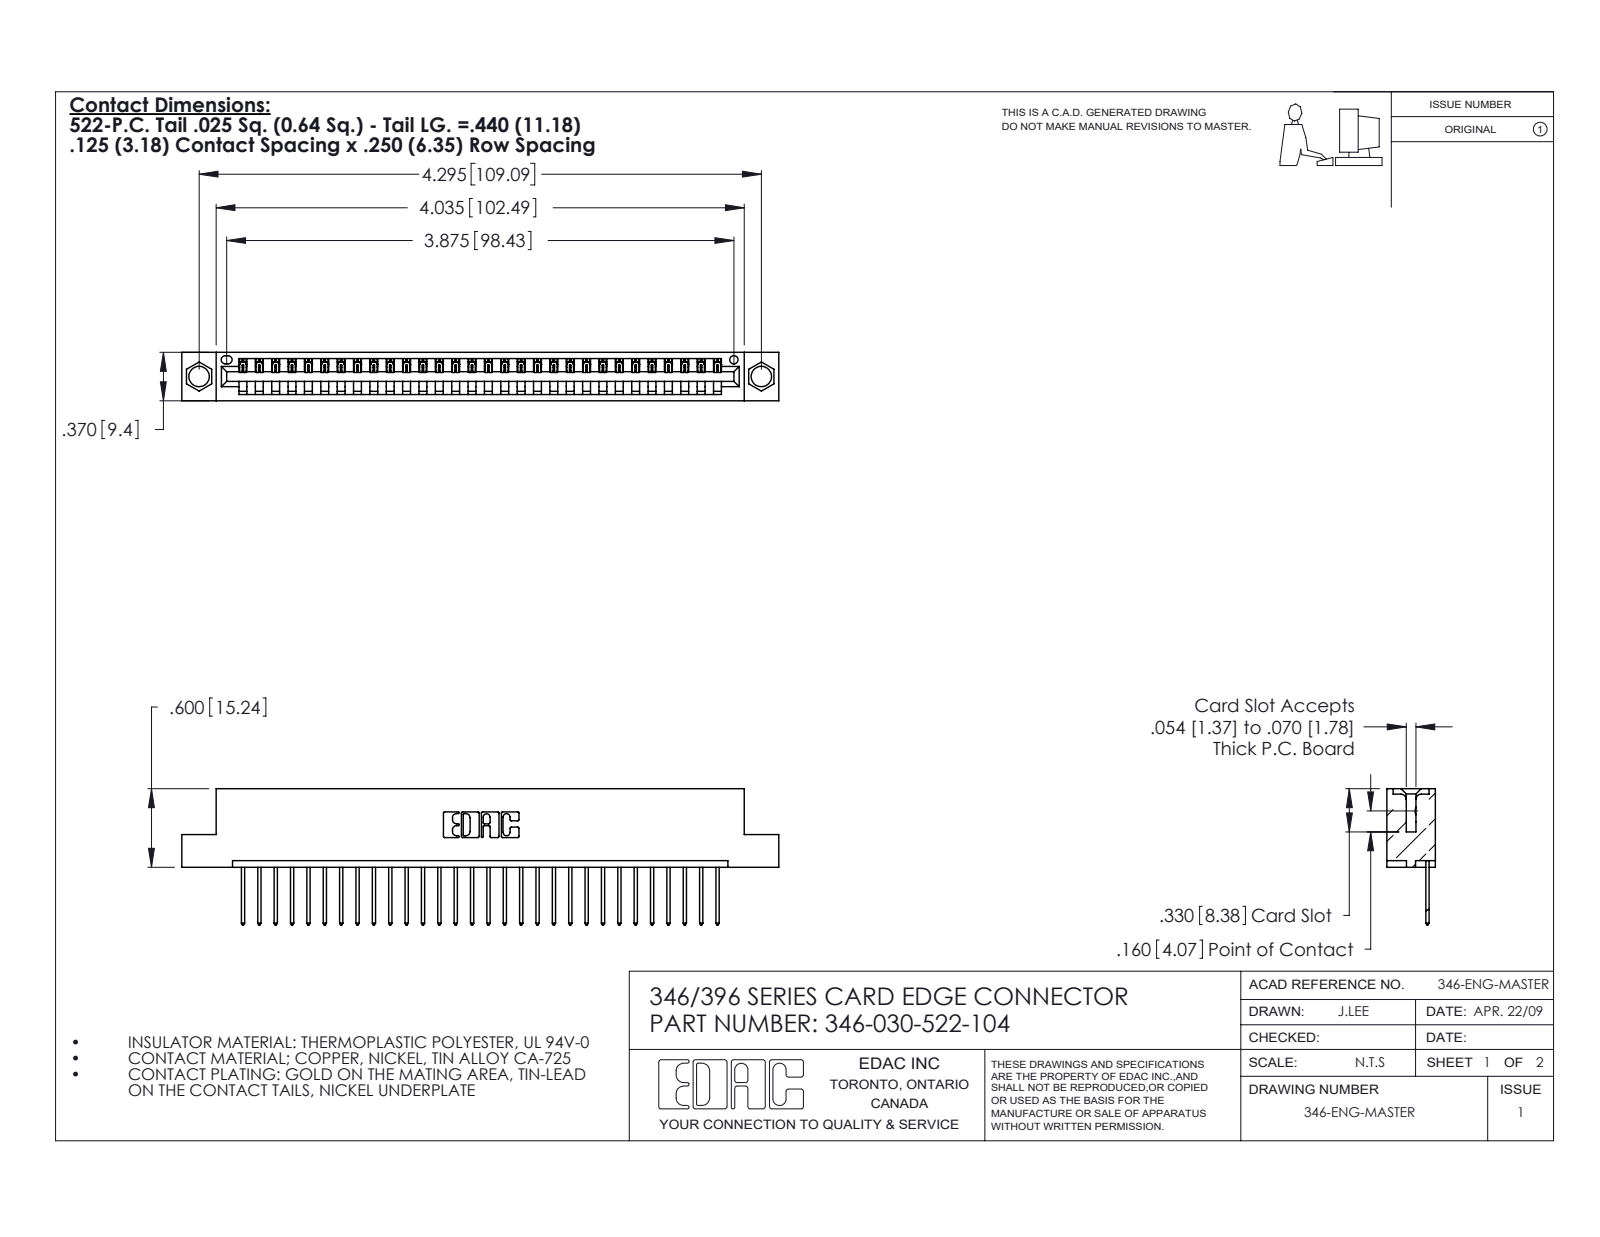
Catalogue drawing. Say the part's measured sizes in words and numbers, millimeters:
The part is named "346 Part_Flush Mounting Lugs - 0.156 Dia-TH; 346-030-522-104; 345-292-001_345-293-122". Its 3-D file was written by "SolidWorks 2020 (CONFIG_CONTROL_DESIGN)". It is 31 solids with 1876 faces: 1290 planar, 586 cylindrical and 0 other. Overall it measures 115.8 by 26.4 by 9.4 millimeters. Its volume is 10 900 cubic millimeters and its surface area 13 450 square millimeters. Round holes: 2 of diameter 4, 1 of diameter 1.6. Partial cylindrical surfaces (rounded edges, fillets, slot ends): 60 of radius 0.2, 60 of radius 0.3, 22 of radius 0.3, 6 of radius 0.2, 6 of radius 0.8, 3 of radius 0.7, 2 of radius 0.8, 2 of radius 1. The main face-to-face distances are 1.2, 8.2, 9.4, 6.4, 1.8, 7.6, 0.6, 3.8, 5.6, 2.5. The hole center spacings are 6.2, 103.8, 109.1.
